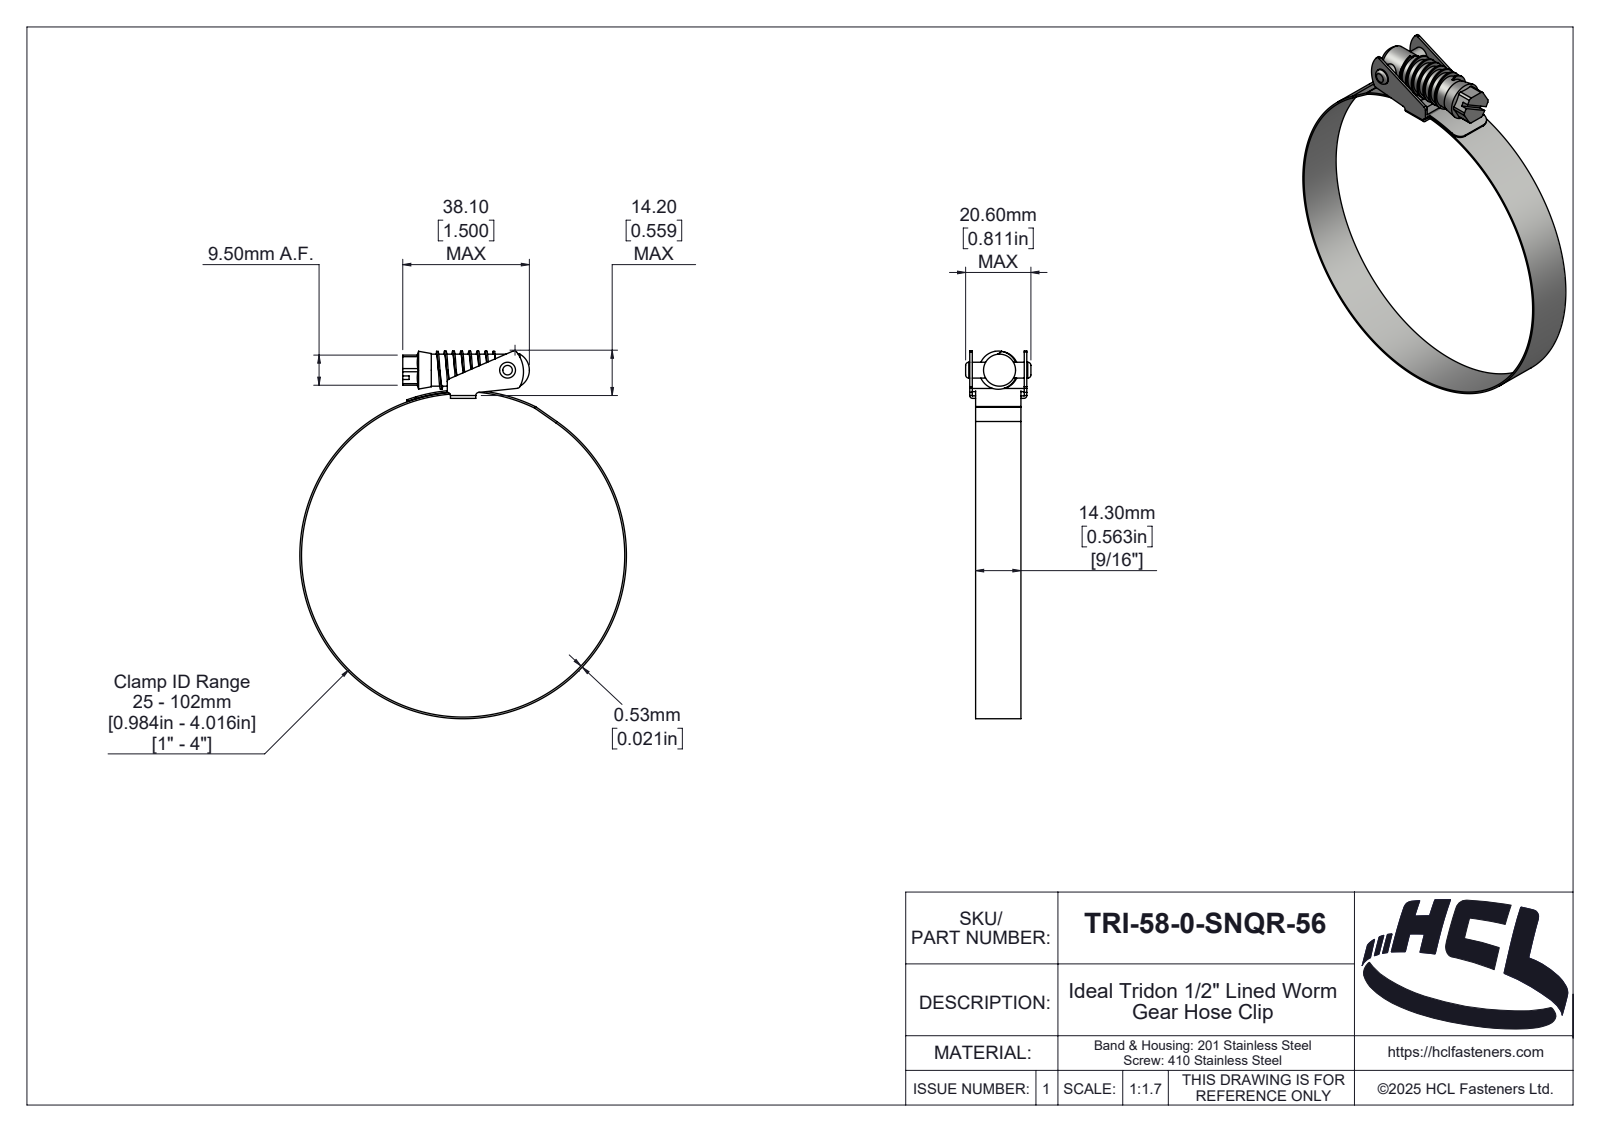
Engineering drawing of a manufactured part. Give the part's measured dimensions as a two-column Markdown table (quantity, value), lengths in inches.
| quantity | value |
| --- | --- |
| part name | TRI-58-0-SNQR-56 |
| STEP written by | SolidWorks 2025 (AUTOMOTIVE_DESIGN) |
| units | inches |
| bodies | 5 solids, 222 faces (44 planar, 112 cylindrical, 66 other) |
| overall size | 4.568 × 4.057 × 0.811 |
| volume | 0.391 in³ |
| surface area | 21.78 in² |
| round holes (diameter × count) | 0.197 × 1, 4.016 × 1 |
| round bosses / shafts (diameter × count) | 4.057 × 1, 0.398 × 1 |
| partial cylindrical surfaces (radius × count) | 0.039 × 11, 0.004 × 2, 0.035 × 2, 0.118 × 2, 0.018 × 1, 0.074 × 1, 0.079 × 1, 0.093 × 1 |
| main face-to-face distances | 0.031, 0.677, 0.073, 0.636, 0.041, 0.604, 0.709, 0.646, 0.563, 0.039 |
| hole center spacings | 2.365 |
